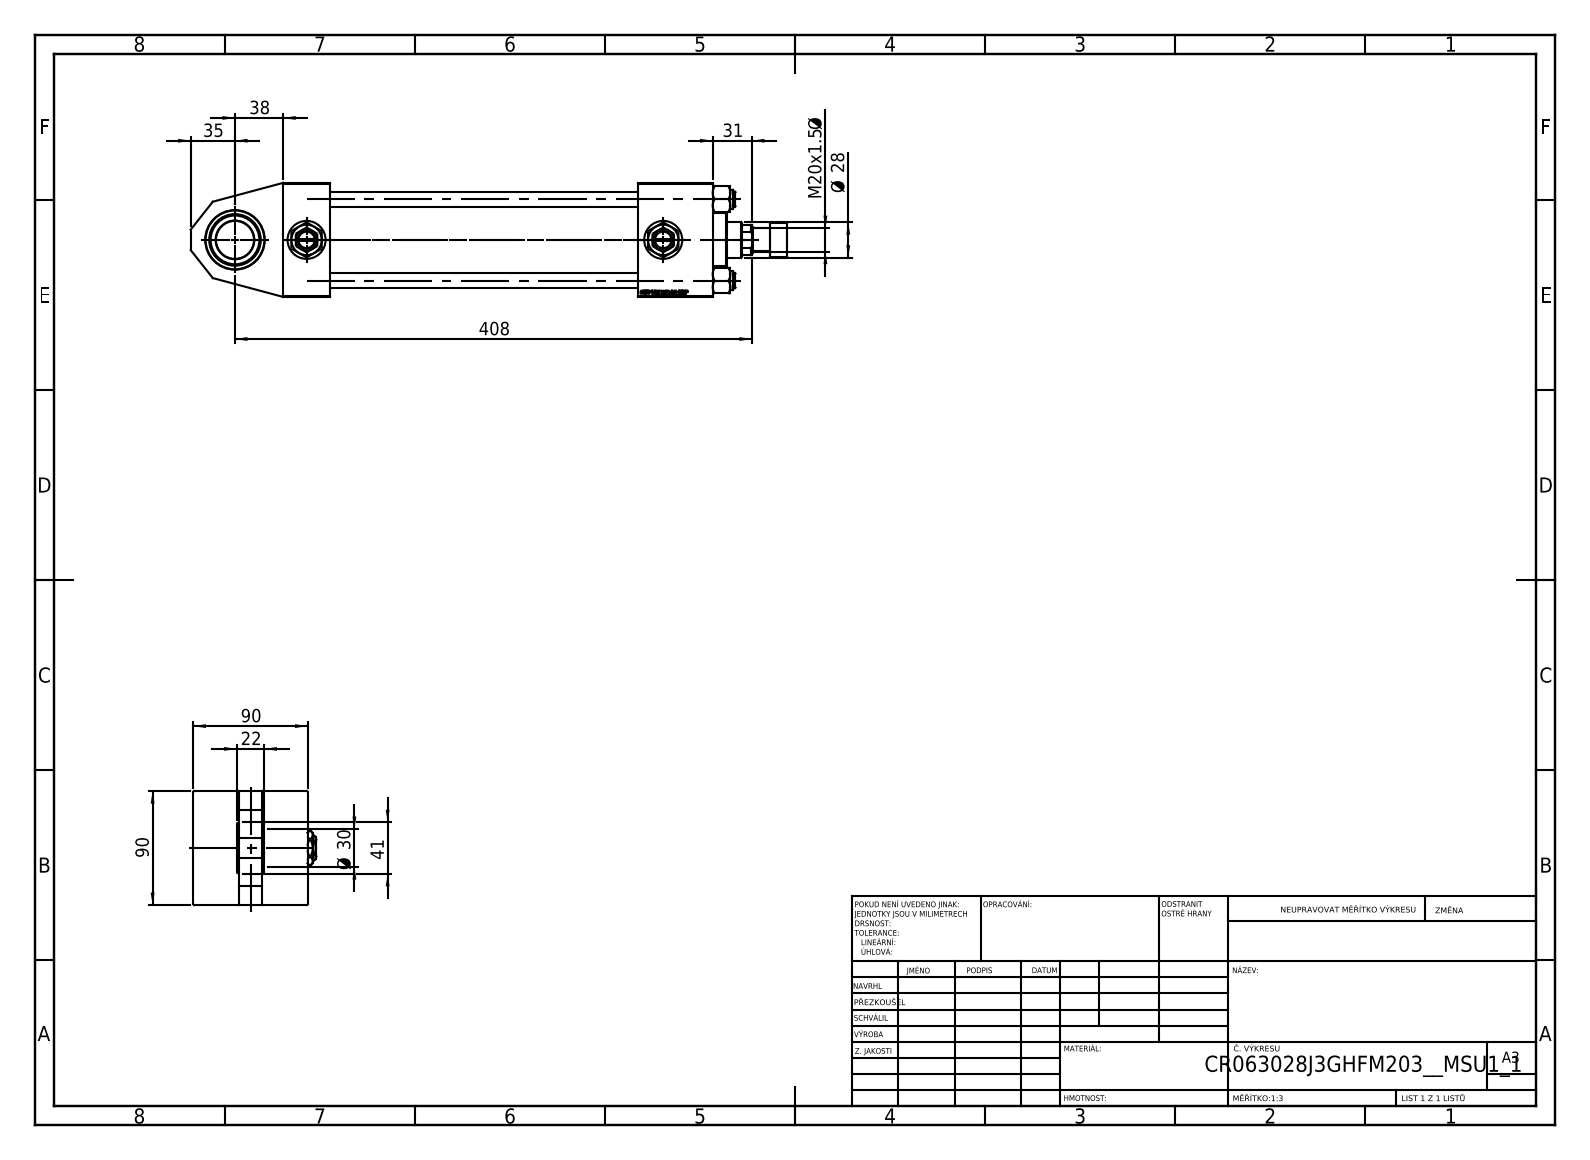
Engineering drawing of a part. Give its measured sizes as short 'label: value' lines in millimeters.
name: V215CR_VCP_J; V215CR_J_Body; Zatka_pro_OIL_PORT; V215CR_J_VNITRNI_KROUZEK (+4 more)
written by: SolidWorks 2019 (CONFIG_CONTROL_DESIGN)
unit: mm
bodies: 15 solids, 1260 faces (568 planar, 104 cylindrical, 588 other)
size: 471 × 97 × 90
volume: 1 347 000 mm³; area: 328 281 mm²
holes: 4× ⌀12, 3× ⌀30, 2× ⌀2.5, 2× ⌀7, 2× ⌀20.96, 1× ⌀18.5, 1× ⌀28, 1× ⌀31, 1× ⌀47, 1× ⌀50, 1× ⌀60, 1× ⌀63
bosses: 4× ⌀15, 1× ⌀69, 1× ⌀42, 1× ⌀27, 1× ⌀18
face distances: 90, 54, 36, 302, 37, 339, 59, 280, 243, 18
hole spacings: 32.39, 45.47, 64.3, 68.42, 28.25, 56.5, 90.93, 281.5
